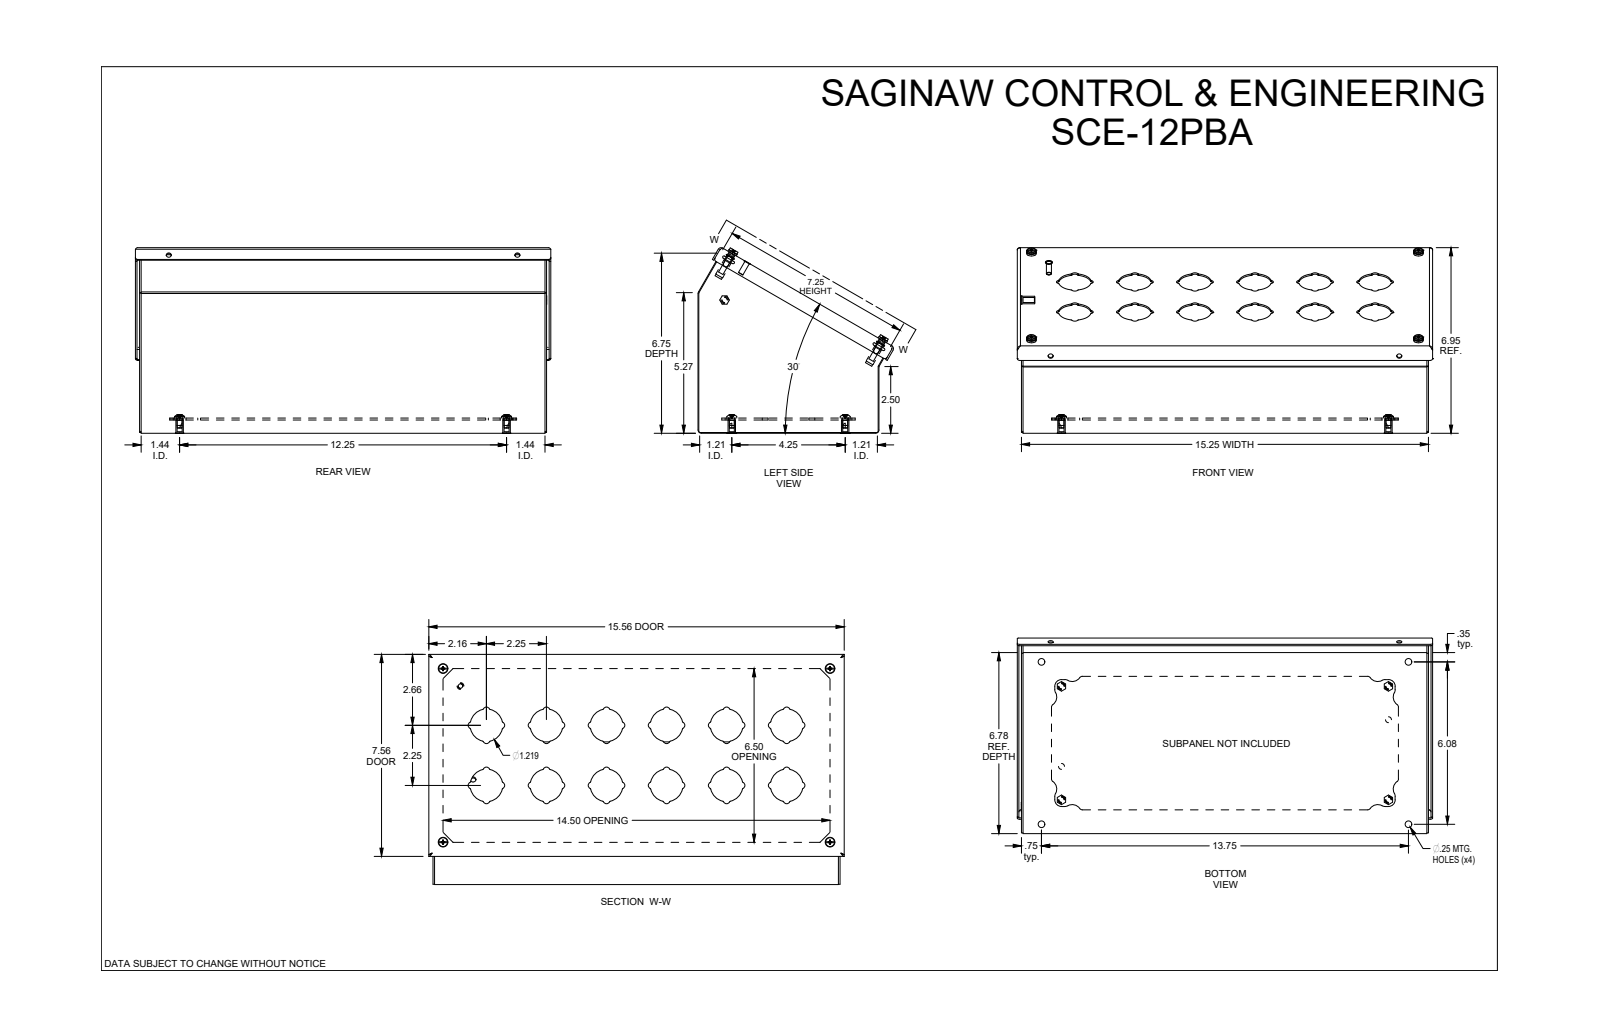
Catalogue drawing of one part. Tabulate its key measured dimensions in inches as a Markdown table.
| quantity | value |
| --- | --- |
| part name | SCE-12PBA |
| STEP written by | SolidWorks 2019 (AUTOMOTIVE_DESIGN) |
| units | inches |
| bodies | 28 solids, 998 faces (341 planar, 399 cylindrical, 258 other) |
| overall size | 15.563 × 7.345 × 6.978 |
| volume | 33.93 in³ |
| surface area | 1 112 in² |
| round holes (diameter × count) | 0.25 × 12, 0.19 × 9, 0.22 × 4, 0.266 × 4, 0.281 × 4, 0.317 × 4, 0.187 × 2, 0.218 × 2, 0.193 × 1 |
| round bosses / shafts (diameter × count) | 0.188 × 9, 0.28 × 5, 0.373 × 4, 0.362 × 4, 0.34 × 4, 0.334 × 4, 0.292 × 4, 0.27 × 4 |
| partial cylindrical surfaces (radius × count) | 0.04 × 100, 0.125 × 56, 0.06 × 20, 0.03 × 12, 0.25 × 12, 0.609 × 12, 0.01 × 10, 0.115 × 8 |
| main face-to-face distances | 0.06, 0.06, 6.72, 0.511, 0.571, 0.075, 0.436, 0.496, 0.059, 6.66 |
| hole center spacings | 14.5, 1.183, 5.219, 13.032, 13.988, 1.25, 2.292, 3 |
